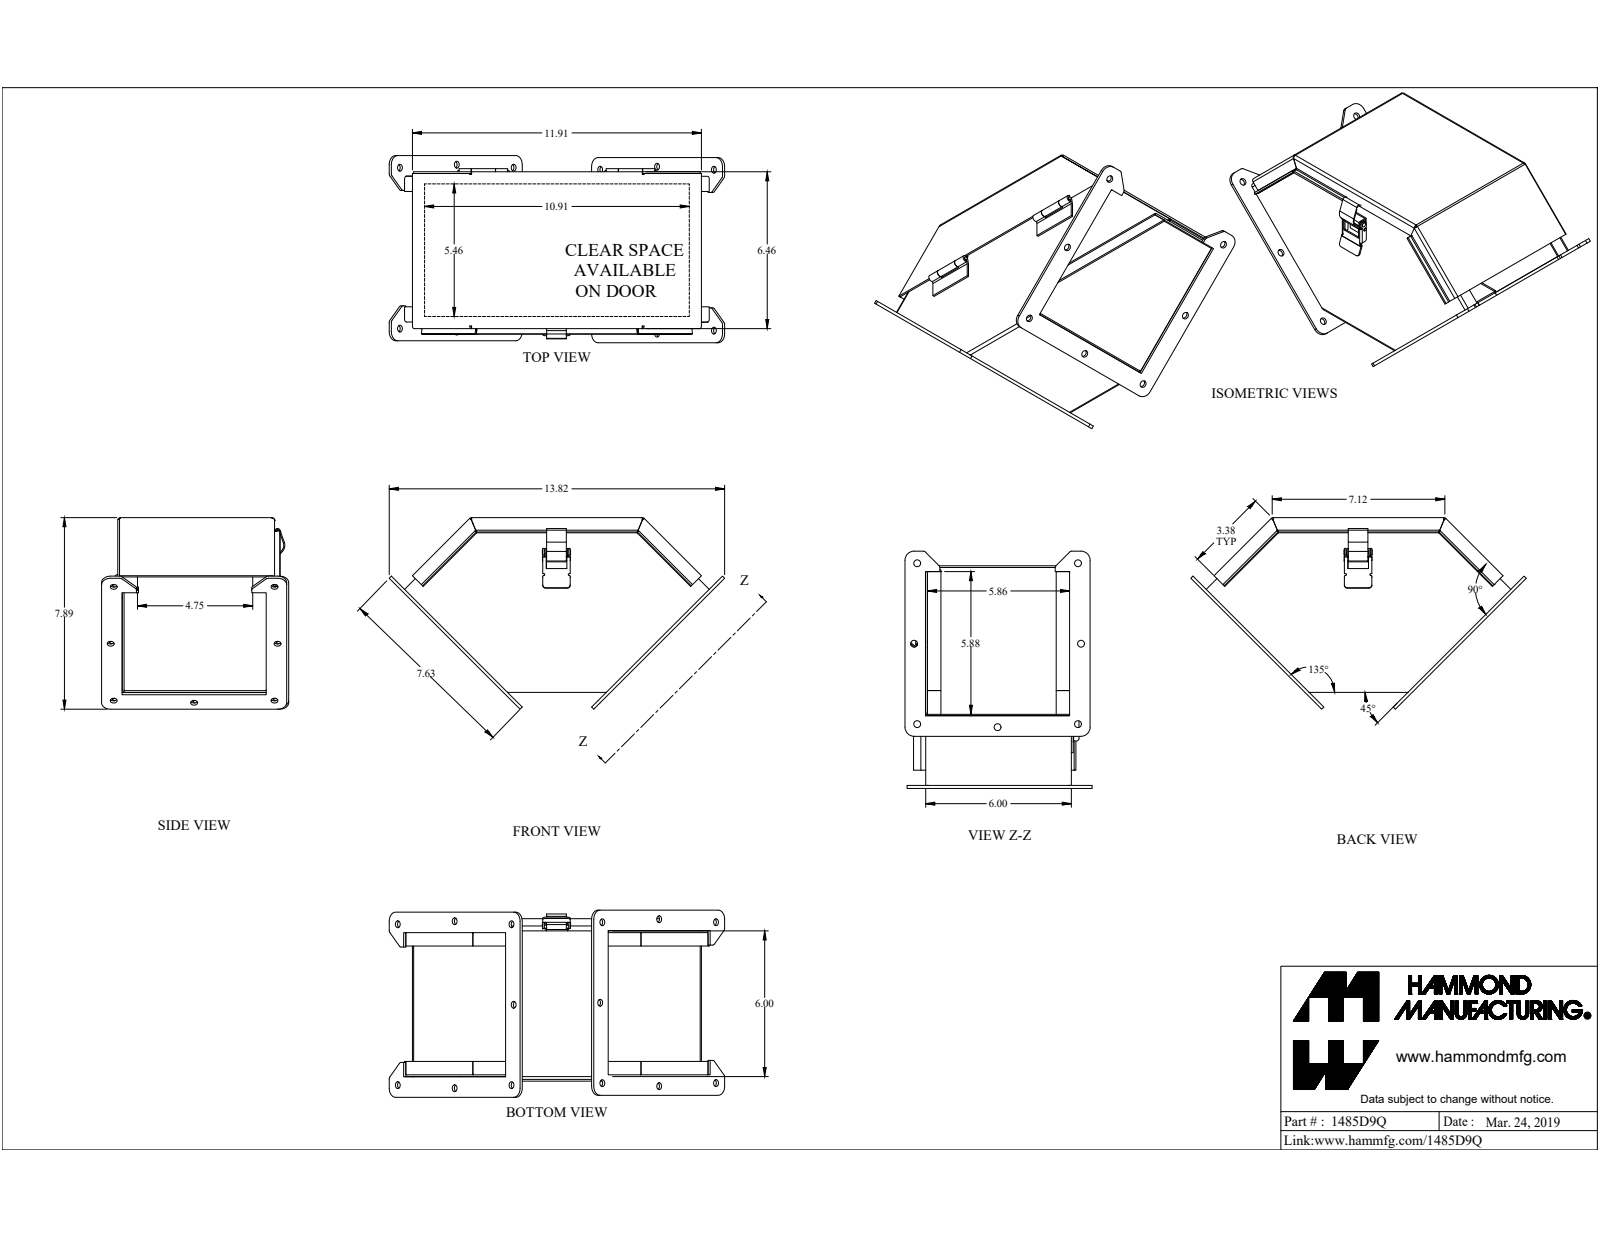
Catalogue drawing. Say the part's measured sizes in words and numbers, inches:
The part is named "1485D9Q". Its 3-D file was written by "SolidWorks 2019 (CONFIG_CONTROL_DESIGN)". It is 13 solids with 378 faces: 228 planar, 130 cylindrical and 20 other. Overall it measures 13.818 by 7.889 by 7.708 inches. Its volume is 25.75 cubic inches and its surface area 690 square inches. Round holes: 14 of diameter 0.281, 1 of diameter 0.125, 1 of diameter 0.13, 1 of diameter 0.164. Round bosses or shafts: 2 of diameter 0.187, 1 of diameter 0.275, 1 of diameter 0.156, 1 of diameter 0.125. Partial cylindrical surfaces (rounded edges, fillets, slot ends): 17 of radius 0.036, 17 of radius 0.108, 11 of radius 0.125, 8 of radius 0.375, 7 of radius 0.016, 3 of radius 0.035, 3 of radius 0.039, 3 of radius 0.076. The main face-to-face distances are 0.072, 5.928, 5.856, 6, 7.125, 6.115, 0.187, 8.971, 9.043, 0.125. The hole center spacings are 3.315, 7.519, 4.861, 6.625, 6.625, 9.369, 3.315, 6.875.
